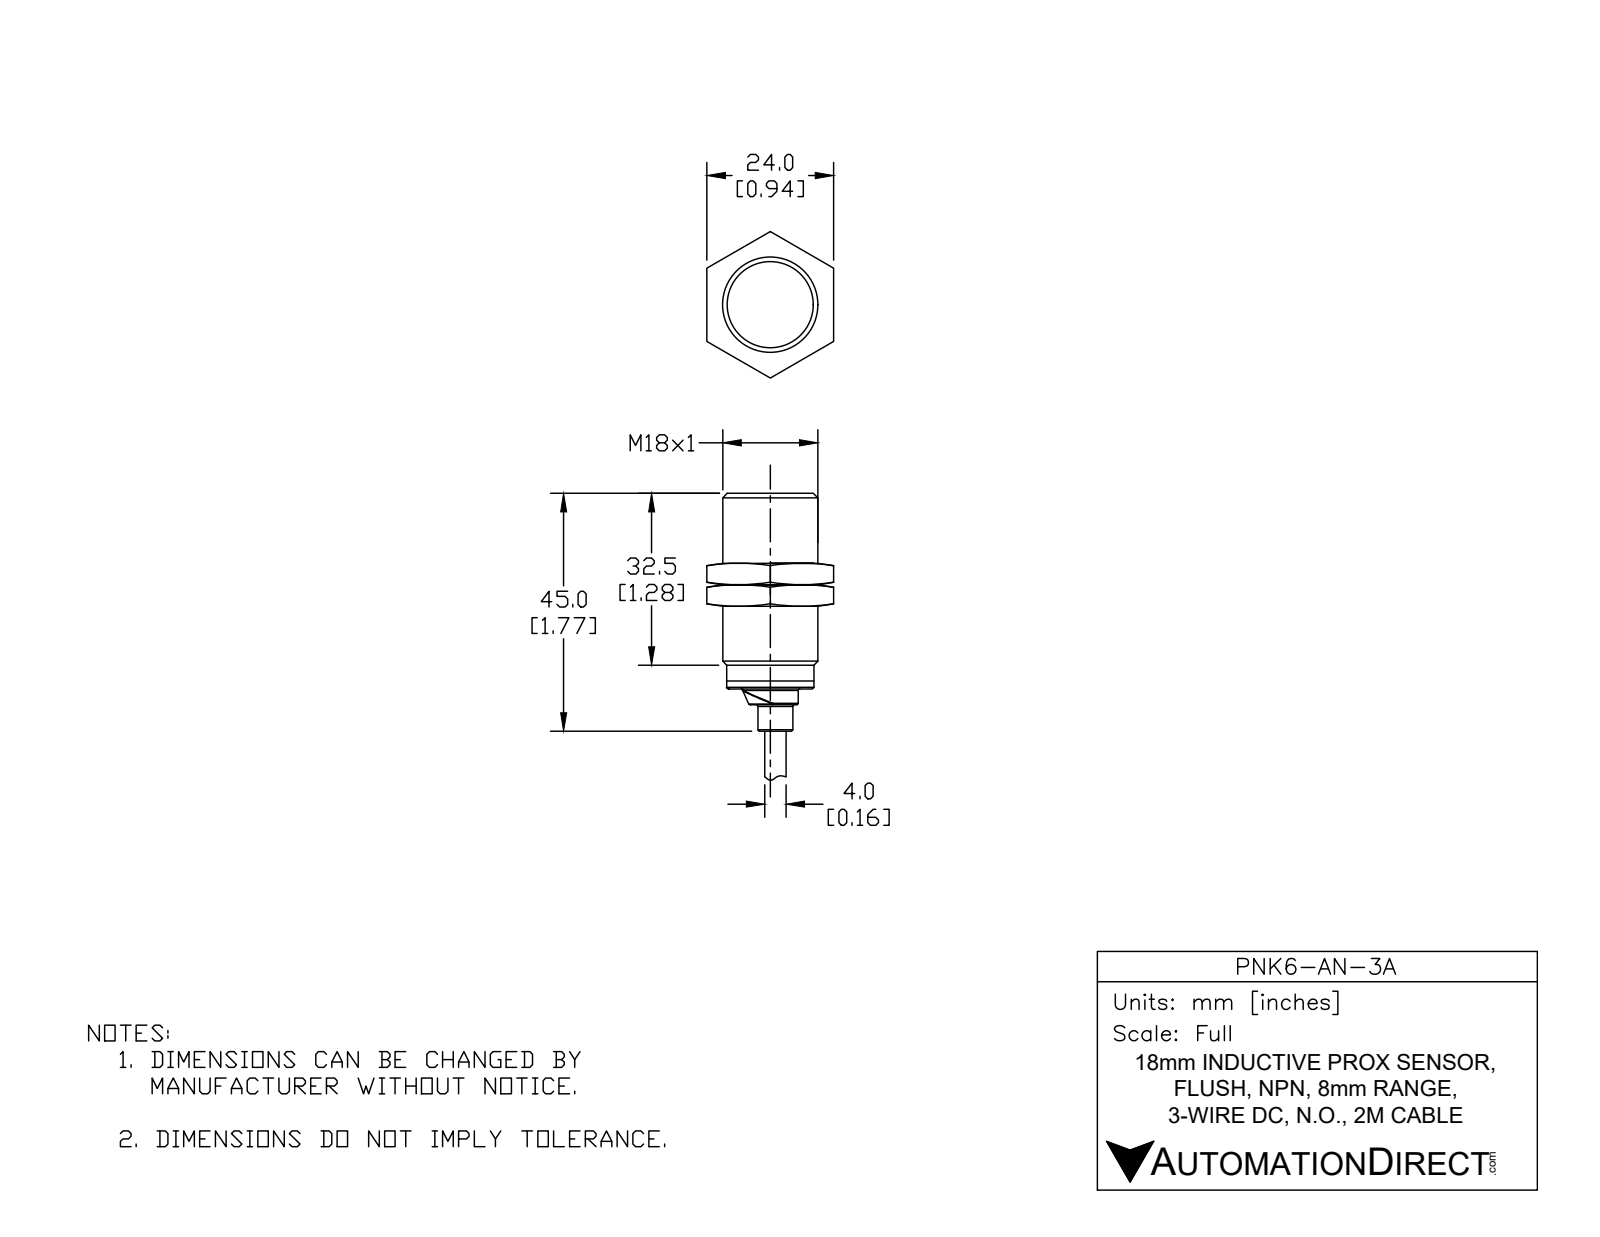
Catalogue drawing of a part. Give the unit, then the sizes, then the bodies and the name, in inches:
Units: inches
Overall size (bounding box): 3.272 × 0.709 × 0.709
Round holes (diameter × count): ⌀0.162 ×1
Round bosses / shafts (diameter × count): ⌀0.049 ×6, ⌀0.709 ×1, ⌀0.65 ×1, ⌀0.65 ×1, ⌀0.417 ×1, ⌀0.26 ×1, ⌀0.157 ×1
Partial cylindrical surfaces — rounded edges, fillets, slot ends (radius × count): R0.146 ×1
Main face-to-face distances: 1.457, 1.398, 0.059, 1.575, 0.177, 0.118, 1.545, 0.148, 0.089, 0.03
Volume: 0.61 in³ · Surface area: 5.425 in²
Bodies: 1 solid, 78 faces (19 planar, 27 cylindrical, 32 other)
Part name (STEP PRODUCT): PNK6-AN-3A
STEP written by: SolidWorks 2017 (AUTOMOTIVE_DESIGN)
